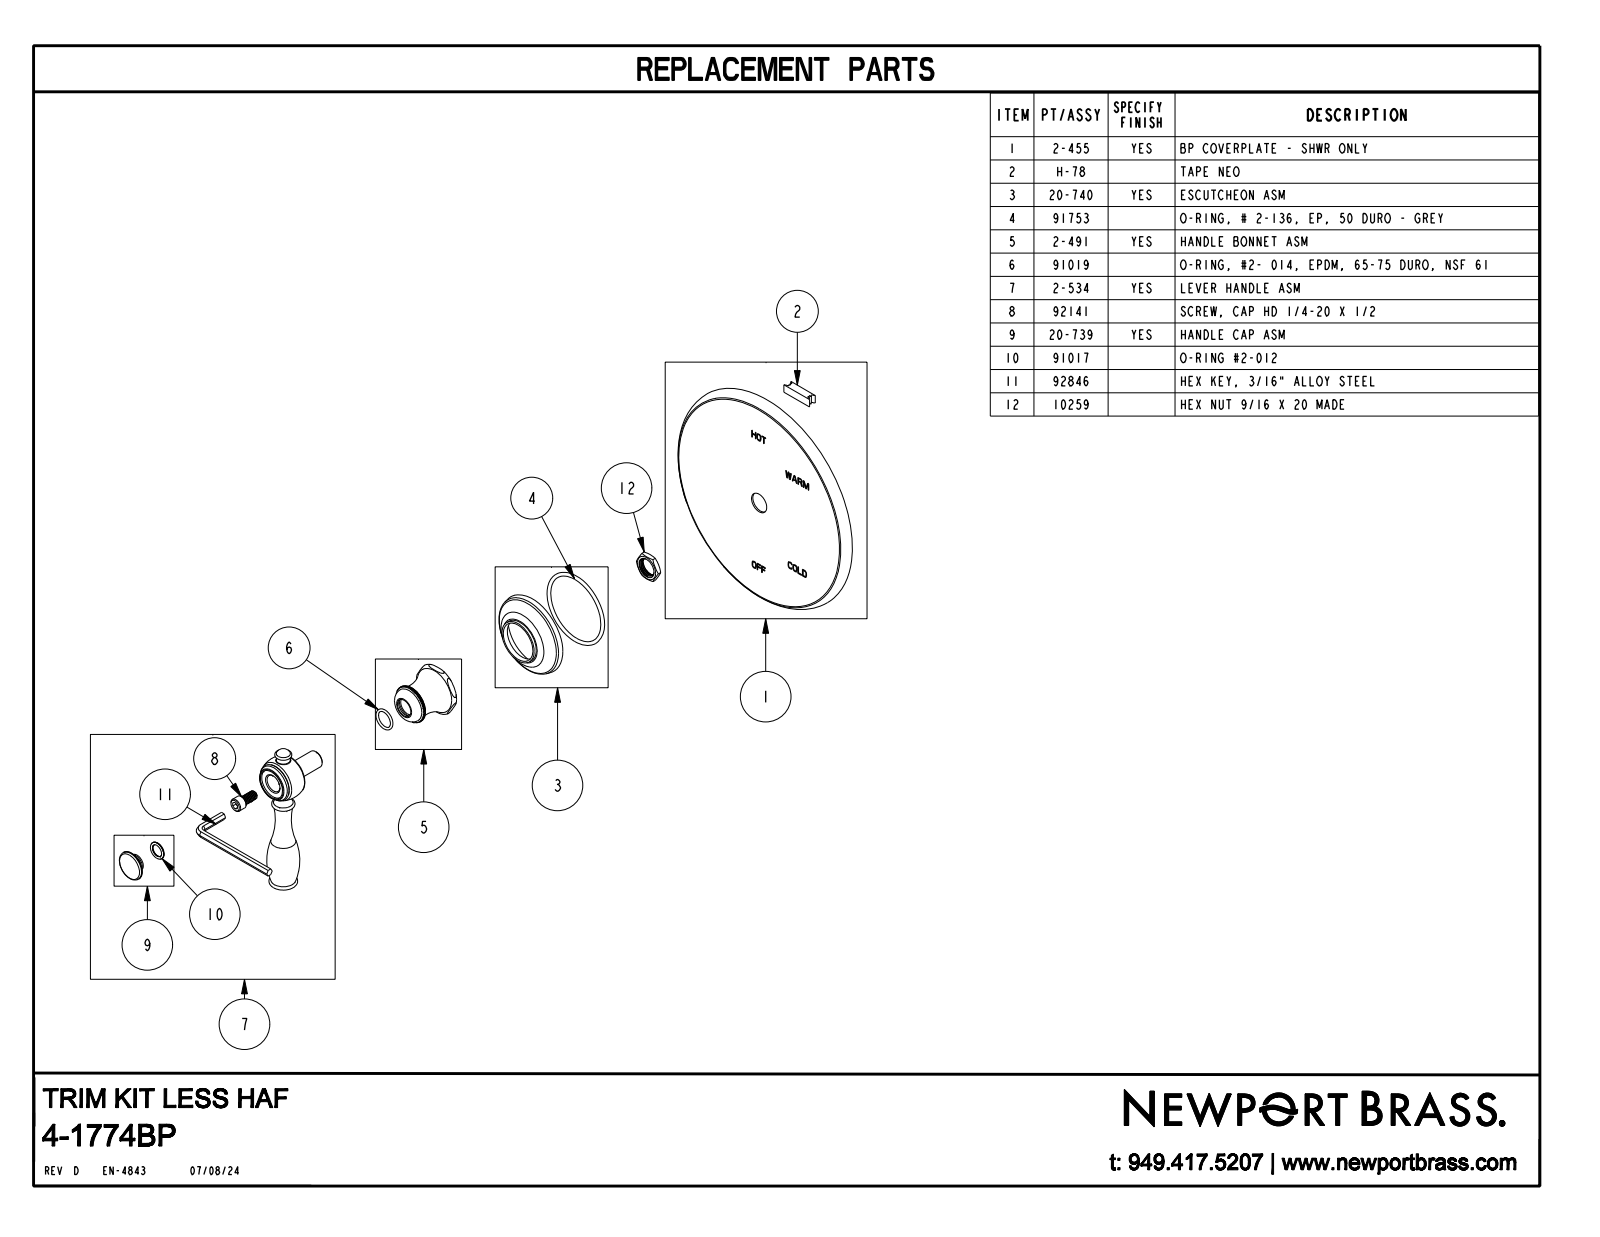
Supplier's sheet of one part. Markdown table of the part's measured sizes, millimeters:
| quantity | value |
| --- | --- |
| part name | 4-1774BP |
| STEP written by | CREO PARAMETRIC BY PTC INC, 2018400 (CONFIG_CONTROL_DESIGN) |
| units | millimeters |
| bodies | 1 solid, 557 faces (483 planar, 14 cylindrical, 60 other) |
| overall size | 176.8 × 168.3 × 94.6 |
| volume | 250 100 mm³ |
| surface area | 59 530 mm² |
| round holes (diameter × count) | 10.4 × 1, 21.7 × 1 |
| round bosses / shafts (diameter × count) | 21.3 × 1, 12.7 × 1, 10 × 1 |
| main face-to-face distances | 8, 72.5, 64.5, 34.9, 7.4, 0.5, 65, 90.5, 83.1, 82.6 |
